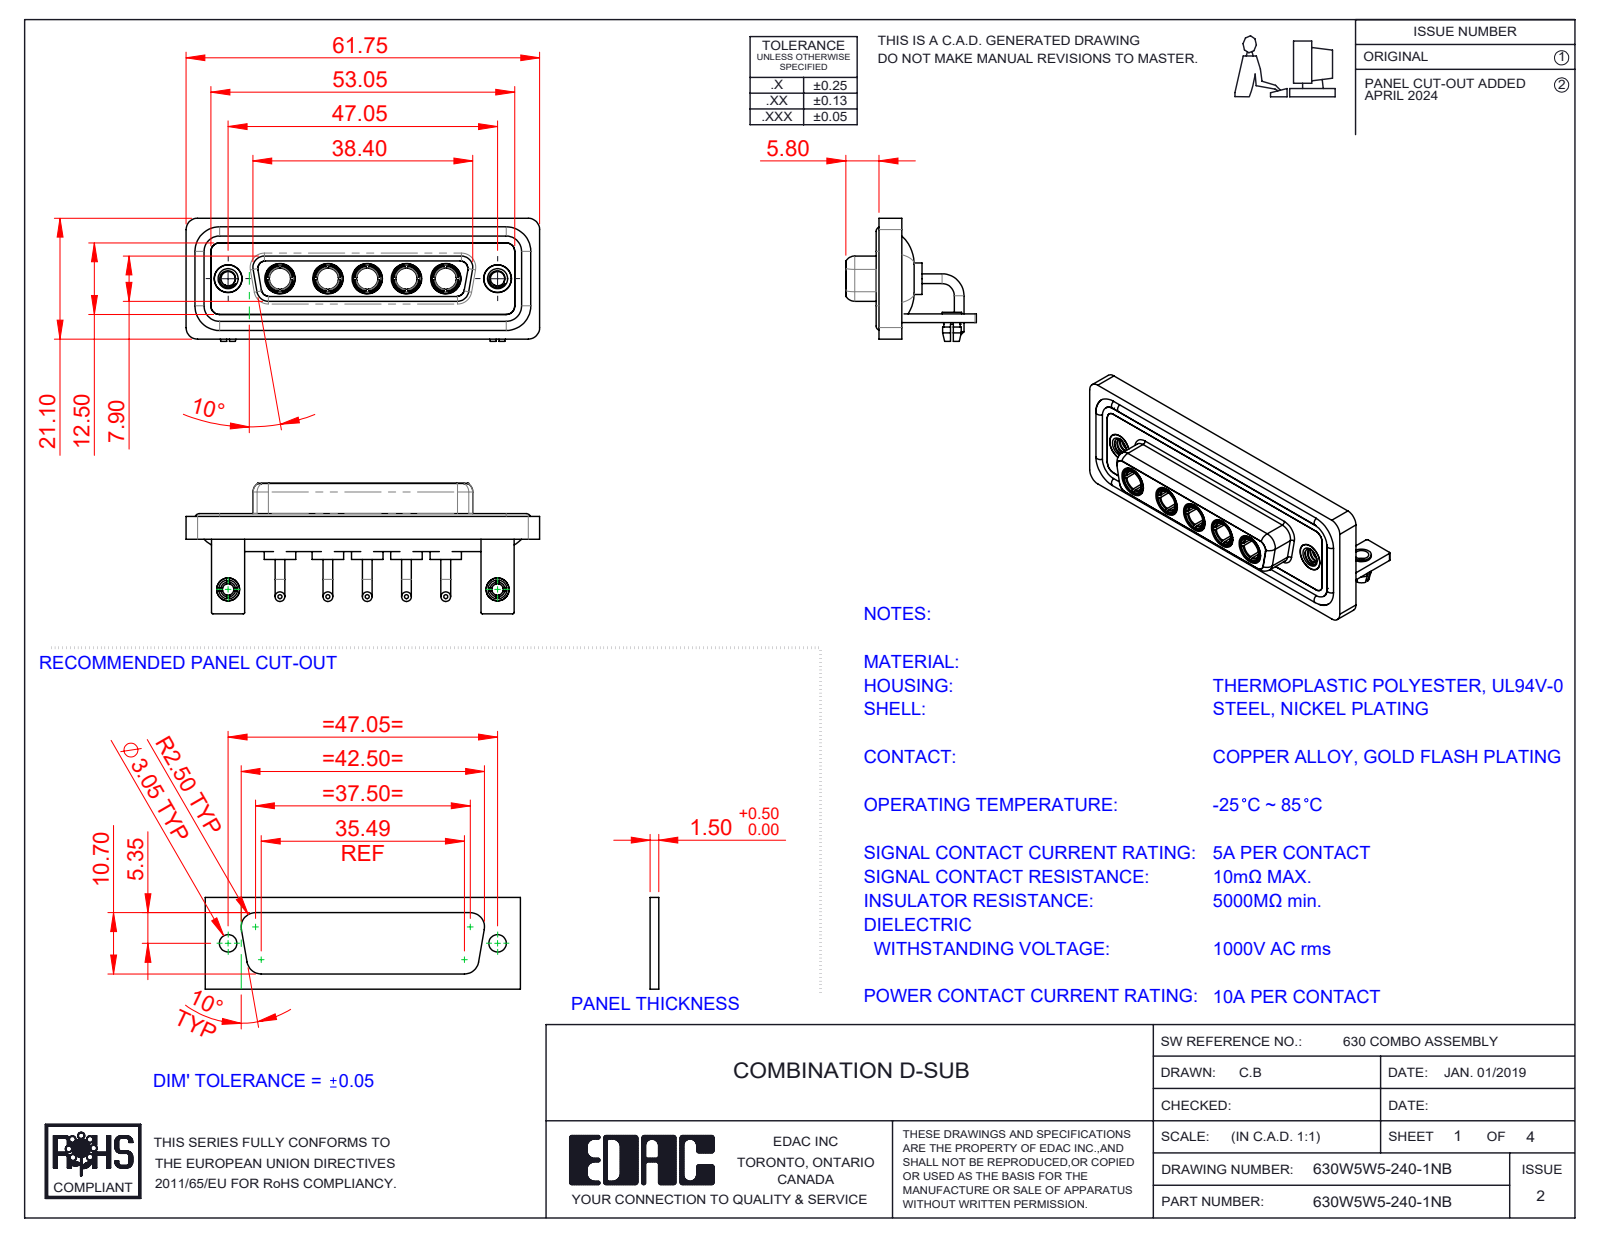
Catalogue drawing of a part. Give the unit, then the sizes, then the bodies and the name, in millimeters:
Units: millimetres
Overall size (bounding box): 61.75 × 22.8 × 21.5
Round holes (diameter × count): ⌀4.85 ×7, ⌀3.7 ×5, ⌀5.3 ×5, ⌀2.5 ×4, ⌀2 ×2, ⌀3.2 ×2, ⌀4 ×2, ⌀4.05 ×2, ⌀5 ×2
Round bosses / shafts (diameter × count): ⌀1.7 ×10, ⌀5.5 ×5, ⌀5.2 ×5, ⌀4.96 ×5, ⌀4.75 ×5, ⌀3.75 ×5, ⌀1.6 ×4, ⌀4.95 ×2
Partial cylindrical surfaces — rounded edges, fillets, slot ends (radius × count): R2 ×19, R1.5 ×18, R0.25 ×16, R1.35 ×8, R1.6 ×8, R0.5 ×5, R2.1 ×5, R0.6 ×4
Main face-to-face distances: 0.4, 1.8, 1.5, 2.9, 3.7, 4.1, 1.1, 1.4, 1.6, 2.5
Hole centre spacings: 6.86, 9.04, 38.01, 47.05, 6.87, 8.38, 13.72, 13.73
Volume: 8 542 mm³ · Surface area: 14 509 mm²
Bodies: 21 solids, 910 faces (318 planar, 367 cylindrical, 225 other)
Part name (STEP PRODUCT): 630Combo Shell Rear_25 Contacts; 630Combo Board Lock_50 Contacts; 630Combo Waterproof Housing_25 Contacts; 630Combo Stabilizer Bracket_50 Contacts (+5 more)
STEP written by: SolidWorks 2023 (CONFIG_CONTROL_DESIGN)
